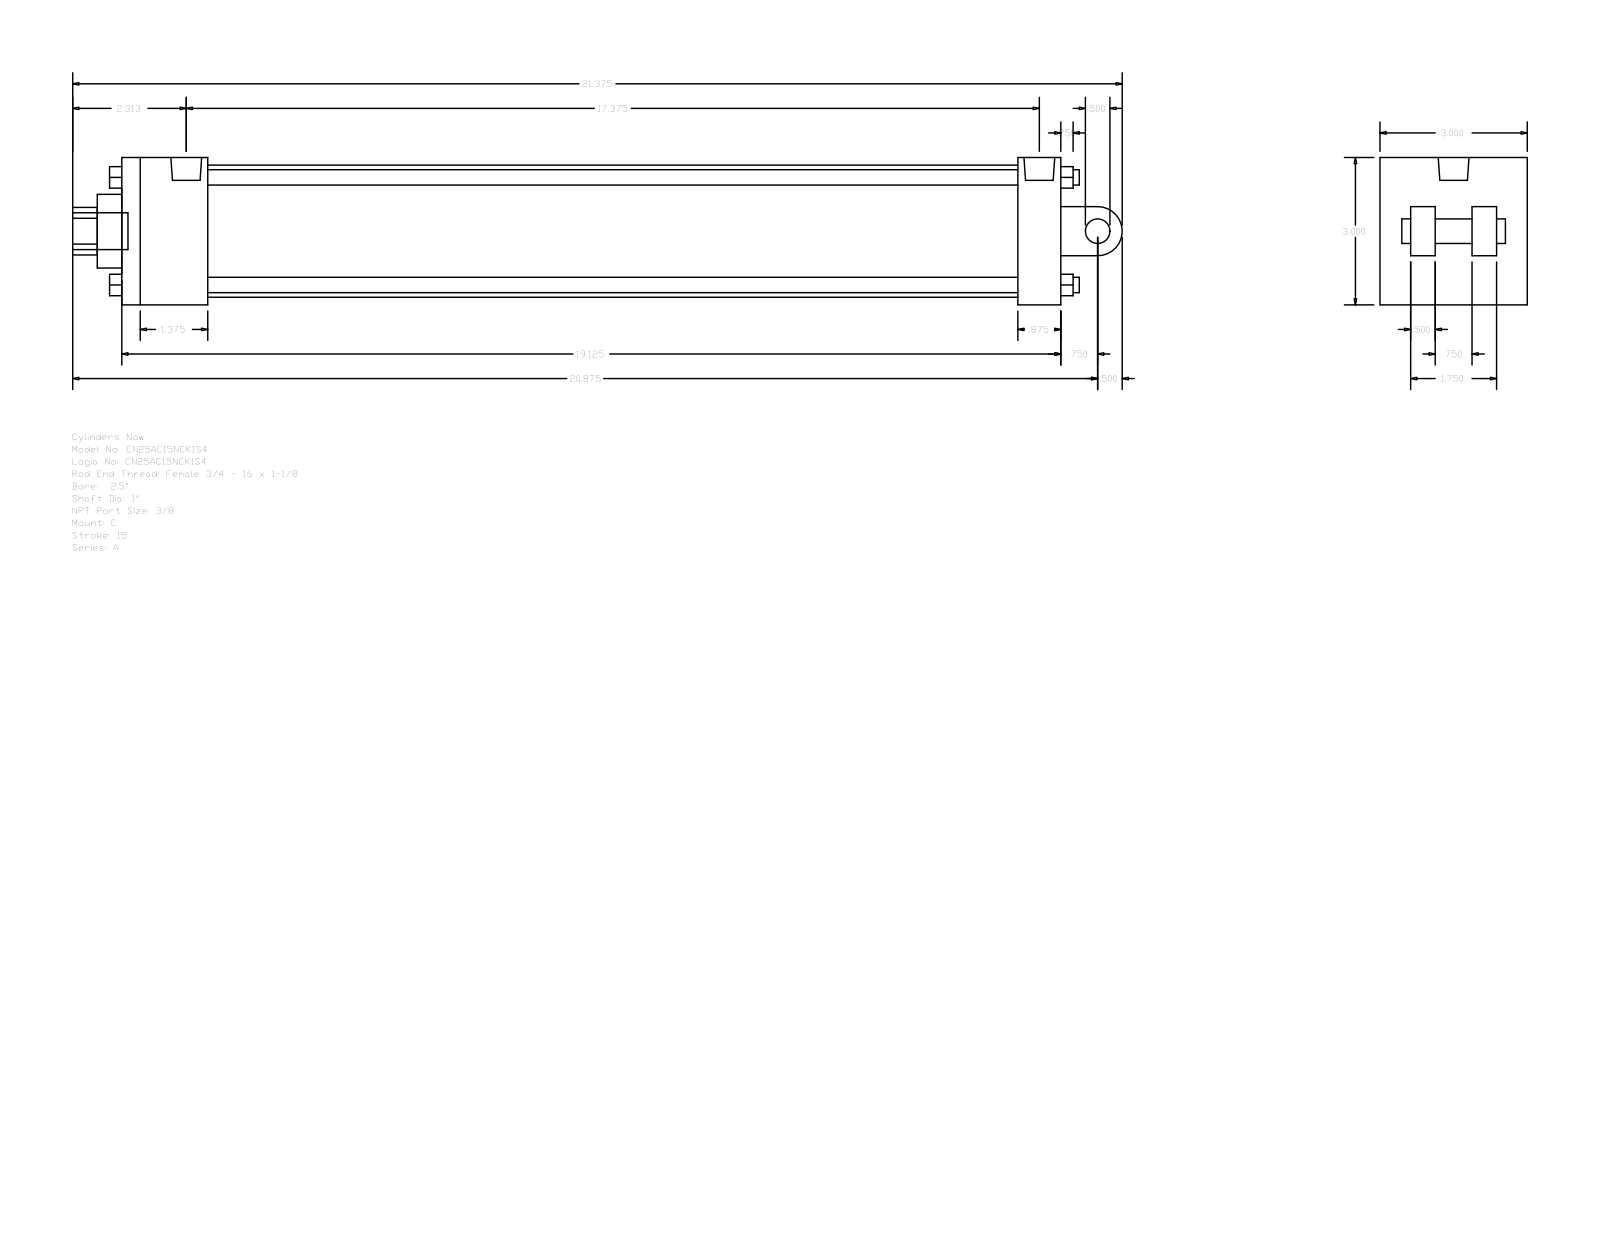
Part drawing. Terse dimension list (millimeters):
name: A_C__0250_1
written by: GSSL Pune (CONFIG_CONTROL_DESIGN)
unit: mm
bodies: 0 solids, 135 faces (102 planar, 33 cylindrical, 0 other)
size: 542.92 × 76.2 × 76.2
holes: 2× ⌀5.56, 1× ⌀15.93, 1× ⌀25.4, 1× ⌀38.1, 1× ⌀68.33
bosses: 4× ⌀7.94, 2× ⌀5.56, 1× ⌀19.05, 1× ⌀15.93, 1× ⌀12.7
rounds: 1× R12.29, 1× R12.7
face distances: 76.2, 485.78, 12.7, 44.45, 463.55, 419.1, 441.33, 22.23, 15.87, 25.4
hole spacings: 2.38
